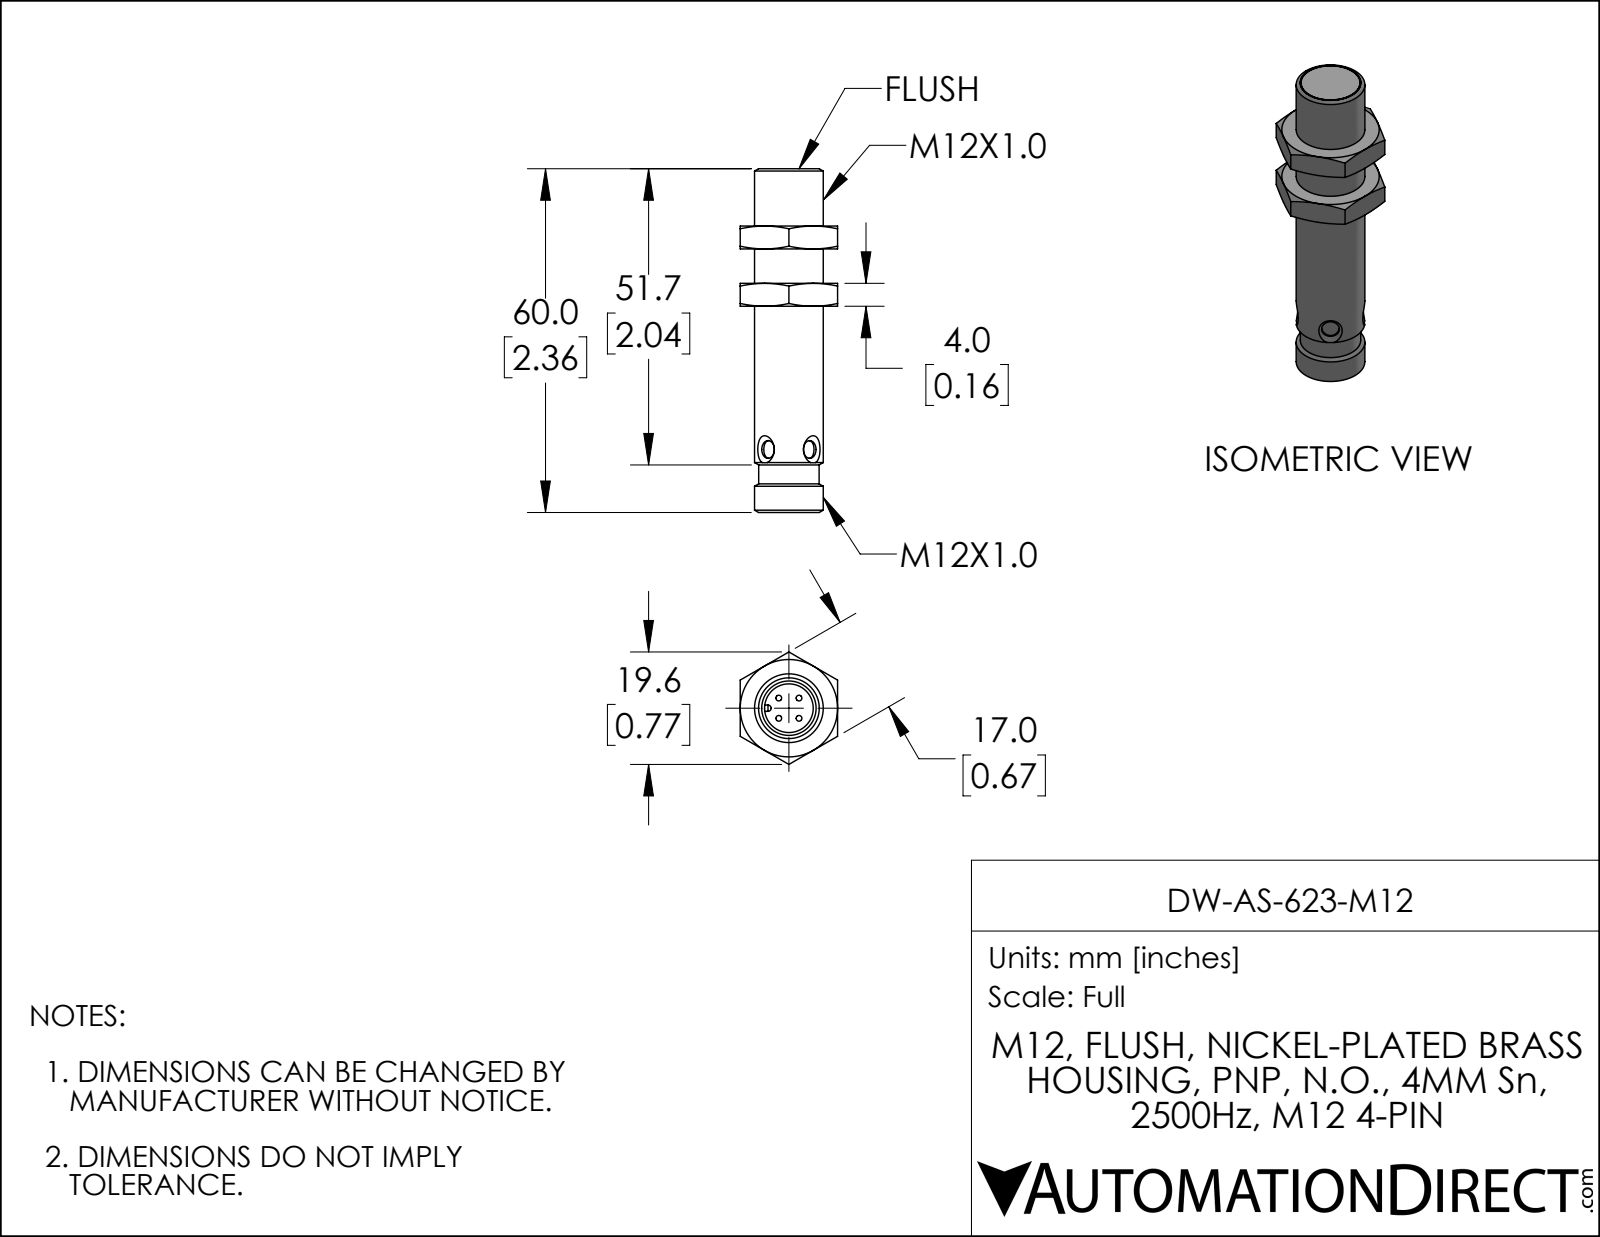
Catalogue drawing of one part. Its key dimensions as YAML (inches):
part_name: "DW-AS-623-M12"
step_written_by: "SolidWorks 2019 (AUTOMOTIVE_DESIGN)"
units: inches
bodies: {solids: 1, faces: 83, planar: 23, cylindrical: 22, other: 38}
overall_size: [2.362, 0.773, 0.669]
volume: 0.443
surface_area: 5.438
round_holes:
  - {diameter: 0.122, count: 2}
  - {diameter: 0.335, count: 1}
  - {diameter: 0.415, count: 1}
round_bosses_or_shafts:
  - {diameter: 0.039, count: 4}
  - {diameter: 0.472, count: 1}
  - {diameter: 0.415, count: 1}
  - {diameter: 0.406, count: 1}
partial_cylinders:
  - {radius: 0.022, count: 2}
  - {radius: 0.193, count: 1}
face_to_face_distances: [0.394, 0.157, 0.669, 0.551, 0.236, 0.787, 0.945, 2.03, 1.636, 1.479]
